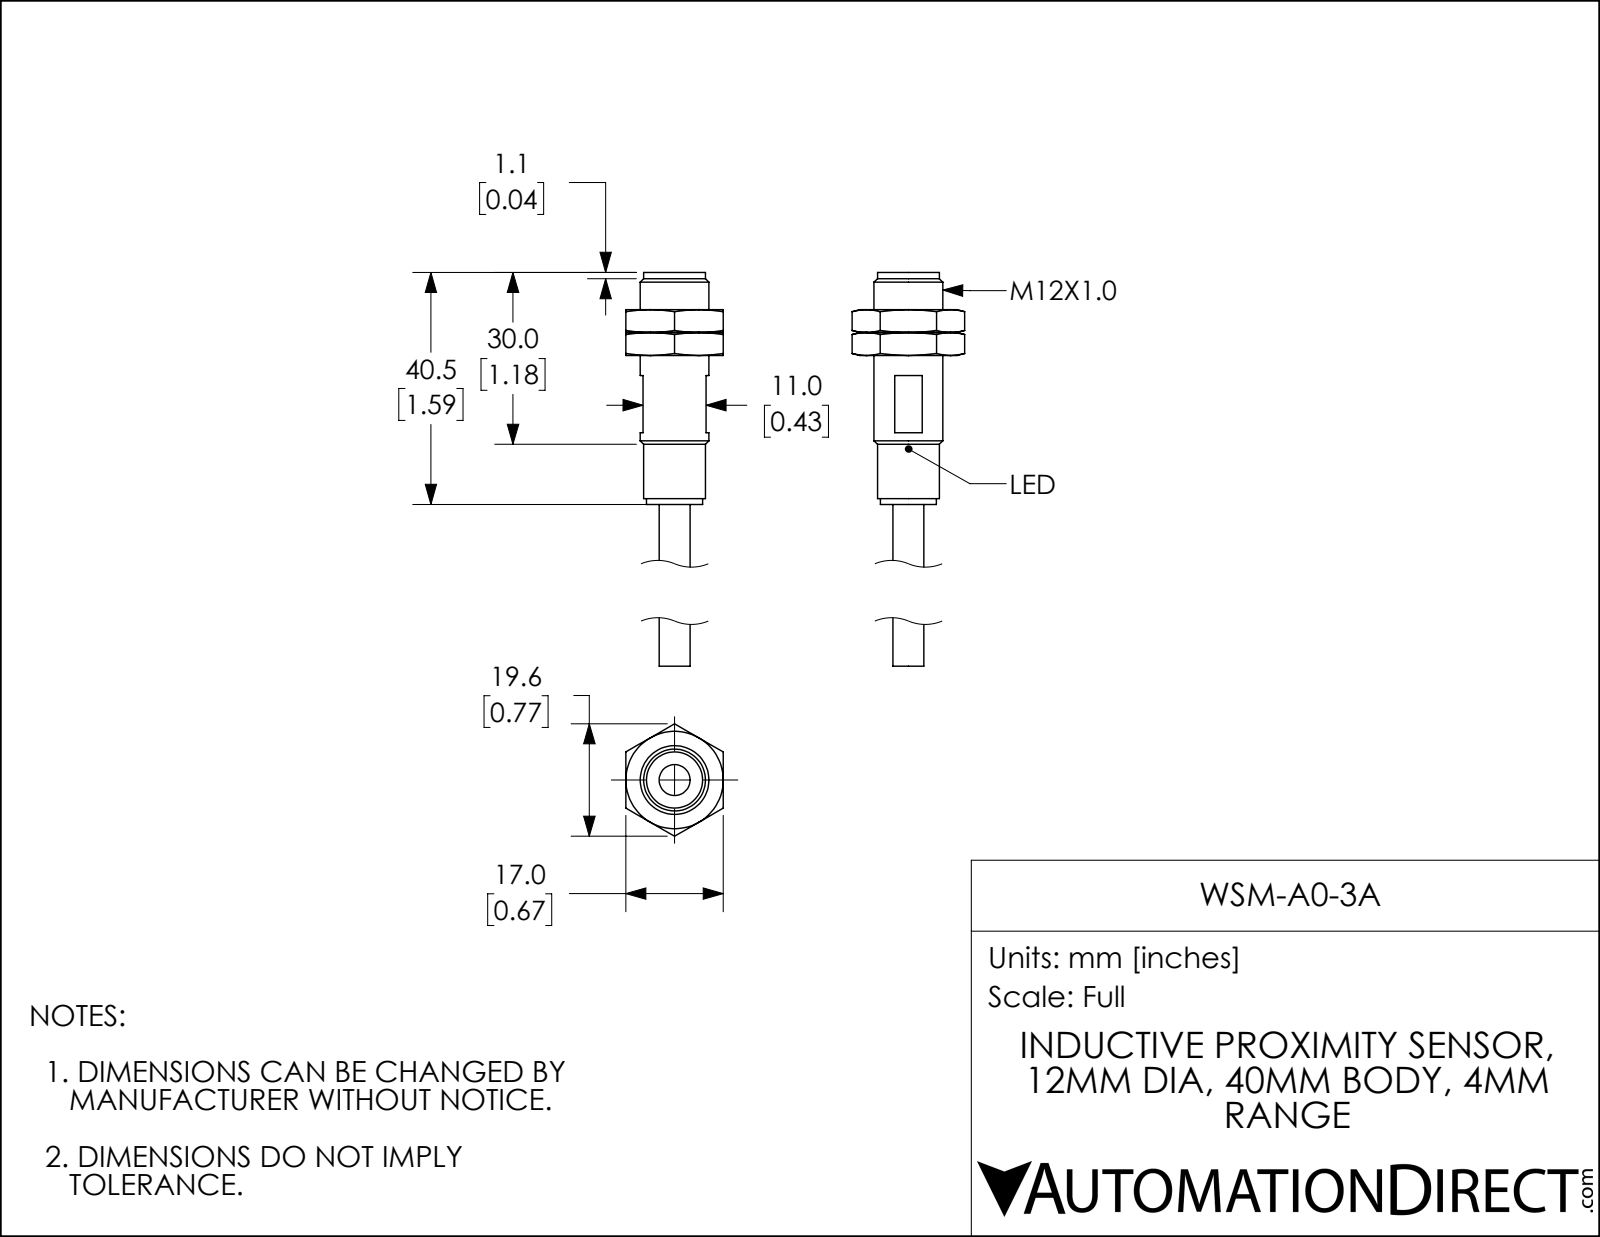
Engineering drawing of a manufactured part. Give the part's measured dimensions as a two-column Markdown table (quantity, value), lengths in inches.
| quantity | value |
| --- | --- |
| part name | WSM-A0-3A |
| STEP written by | SolidWorks 2017 (AUTOMOTIVE_DESIGN) |
| units | inches |
| bodies | 3 solids, 65 faces (28 planar, 7 cylindrical, 30 other) |
| overall size | 2.854 × 0.773 × 0.669 |
| volume | 0.38 in³ |
| surface area | 5.474 in² |
| round holes (diameter × count) | 0.43 × 1 |
| round bosses / shafts (diameter × count) | 0.472 × 1, 0.425 × 1, 0.386 × 1, 0.213 × 1 |
| main face-to-face distances | 0.157, 0.669, 0.315, 0.118, 0.551, 0.413, 0.571, 0.256, 1.181, 1.024 |
